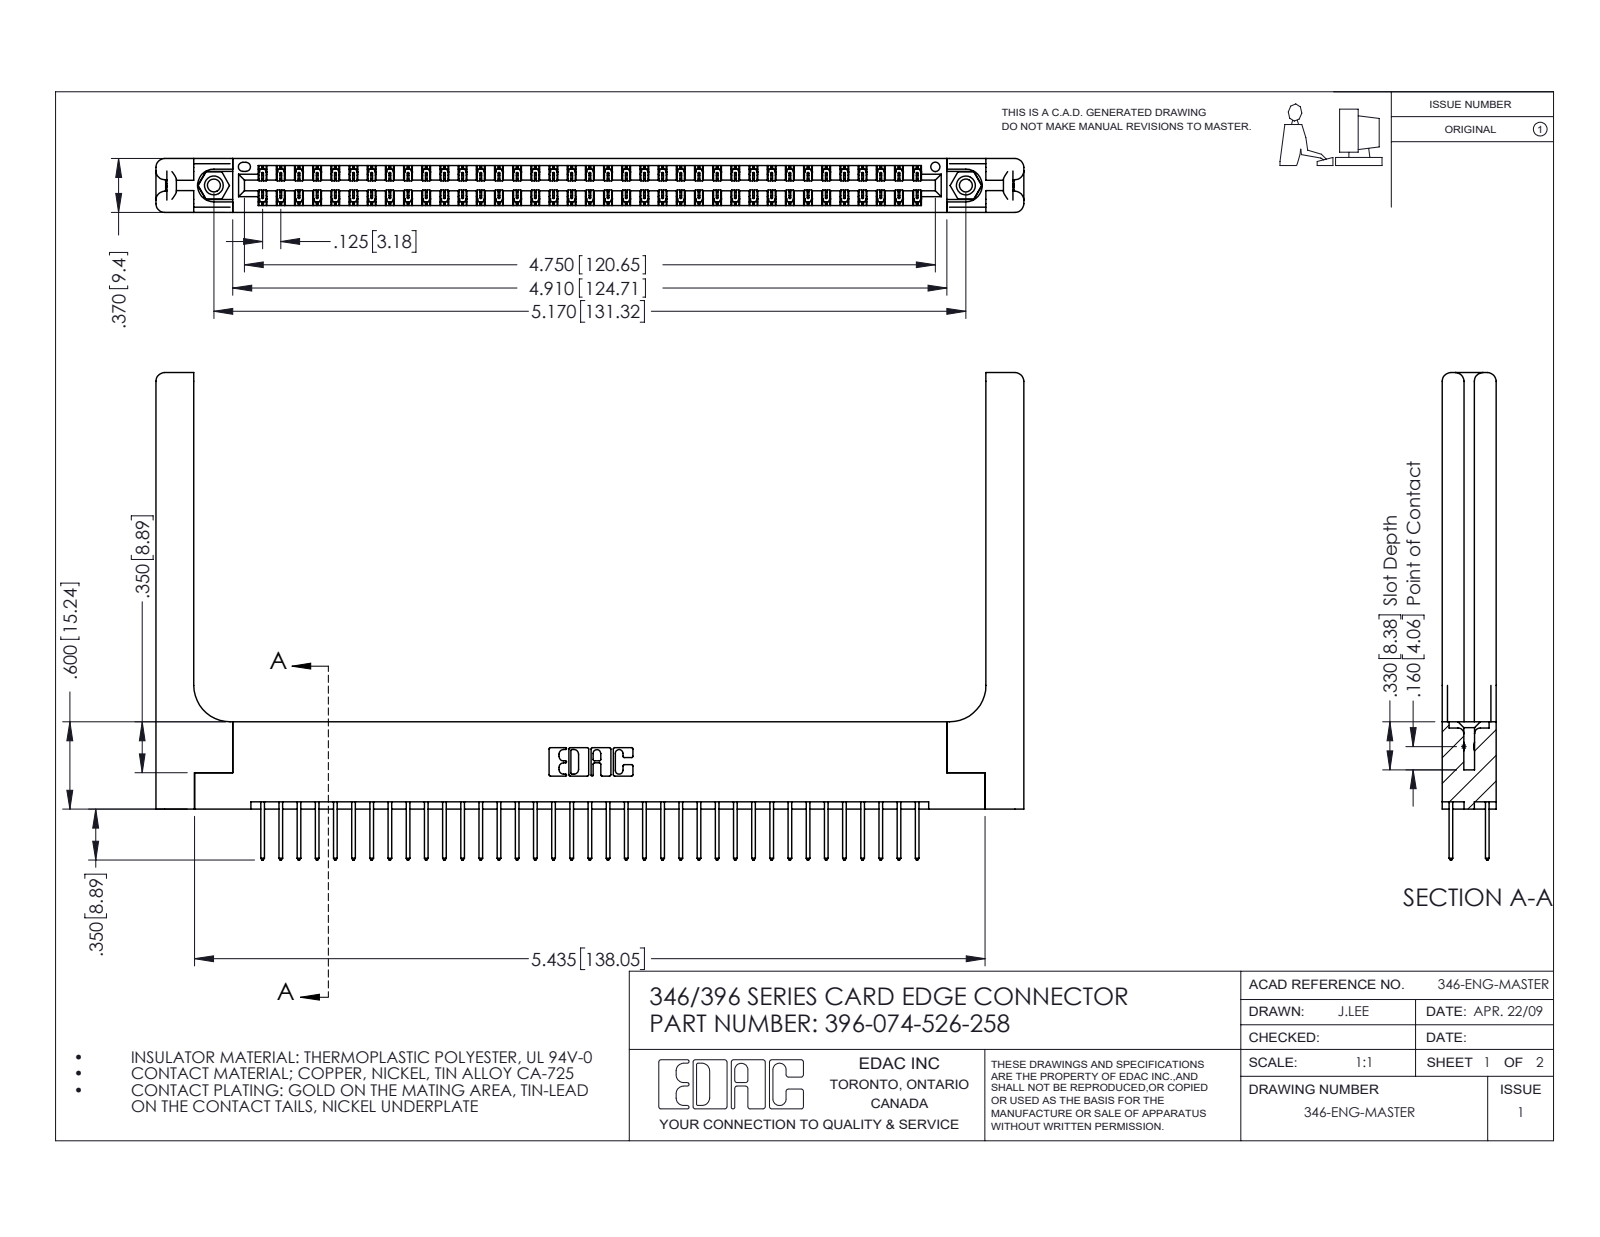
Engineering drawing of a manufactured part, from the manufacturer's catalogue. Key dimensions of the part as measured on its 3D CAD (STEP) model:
Part name (STEP PRODUCT): 346-220-058_345-220-058; 396-074-526-258; 345-292-001_345-293-126; 346 Part_Flush Mounting Lugs - 0.156 Dia-TH (+1 more)
STEP written by: SolidWorks 2016 (CONFIG_CONTROL_DESIGN)
Units: inches
Bodies: 79 solids, 4226 faces (2814 planar, 1352 cylindrical, 60 other)
Overall size (bounding box): 5.966 × 3.35 × 0.37
Volume: 1.364 in³ · Surface area: 40.09 in²
Round holes (diameter × count): ⌀0.089 ×2, ⌀0.125 ×2, ⌀0.156 ×2, ⌀0.064 ×1
Round bosses / shafts (diameter × count): ⌀0.155 ×2
Partial cylindrical surfaces — rounded edges, fillets, slot ends (radius × count): R0.006 ×111, R0.01 ×74, R0.01 ×22, R0.06 ×16, R0.007 ×6, R0.031 ×6, R0.026 ×3, R0.014 ×2
Main face-to-face distances: 0.048, 0.322, 0.37, 0.072, 0.25, 0.148, 0.15, 0.025, 0.298, 0.275
Hole centre spacings: 0.246, 4.961, 5.17
